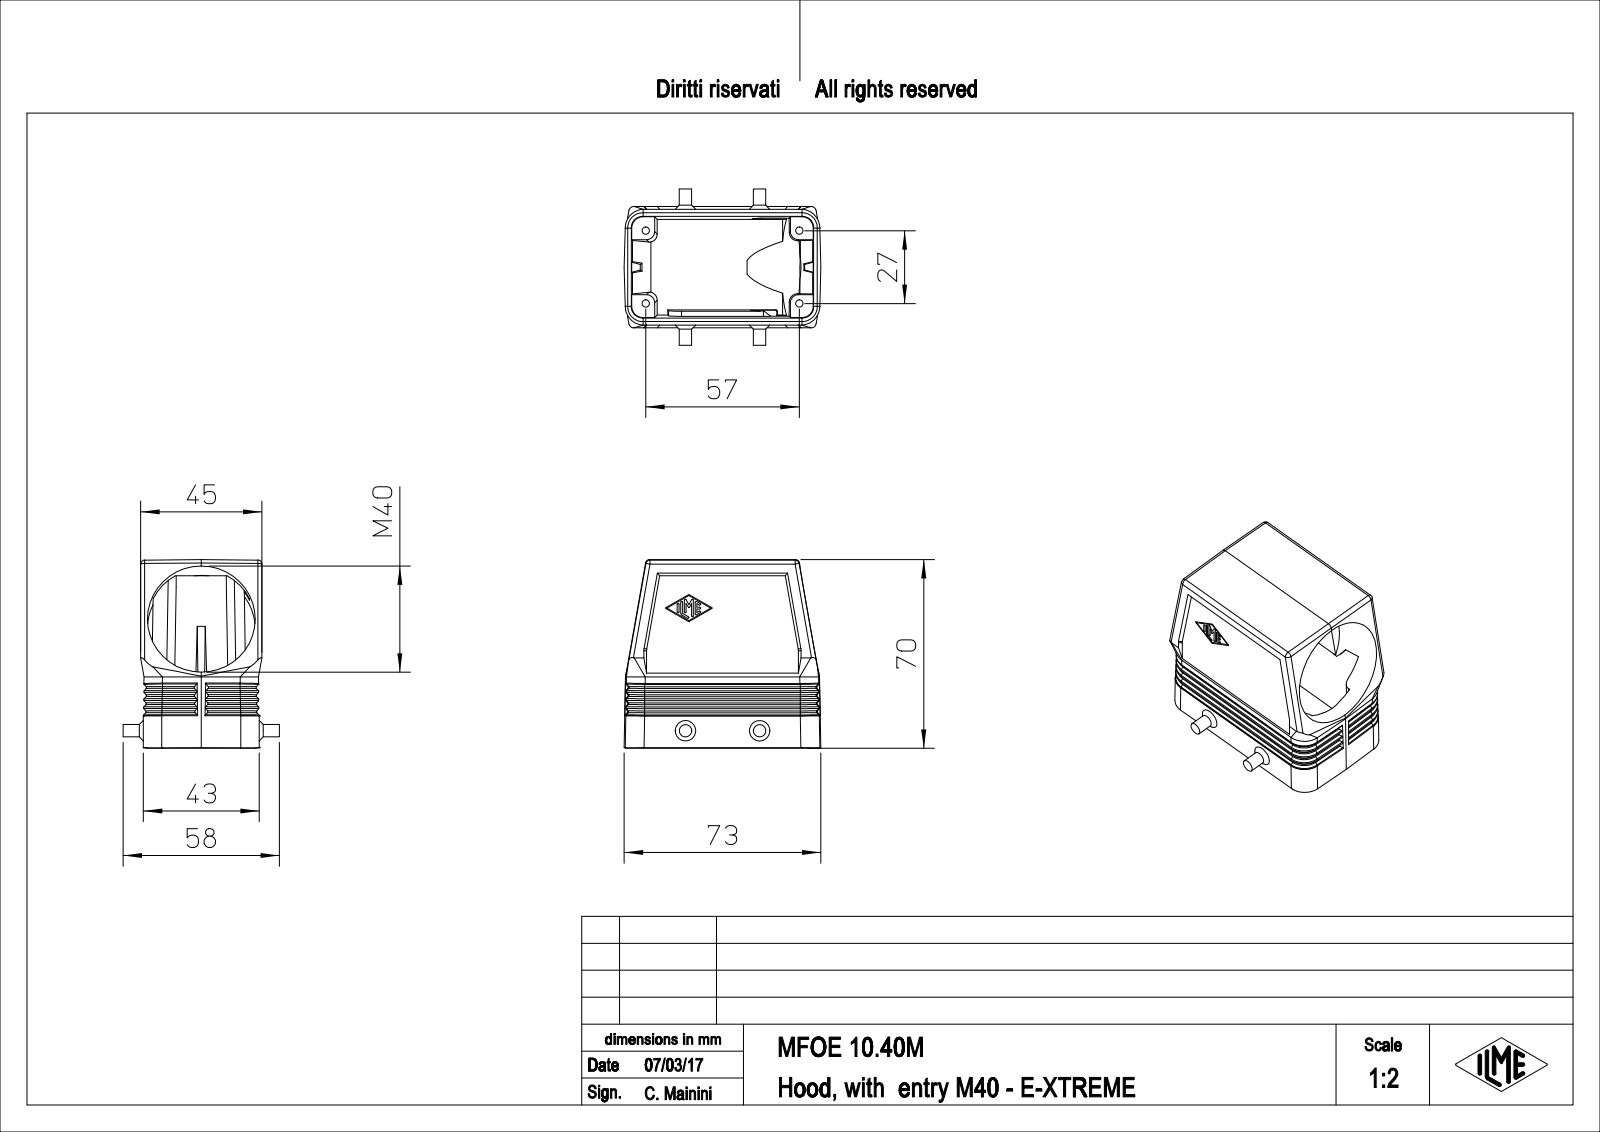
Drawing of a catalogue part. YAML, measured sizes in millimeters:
part_name: "MFOE_10.40M"
step_written_by: "PTC Creo Elements/Direct Modeling 19.0E 27-Jun-2016 (C) Parametric Technology GmbH (AUTOMOTIVE_DESIGN)"
units: millimeters
bodies: {solids: 1, faces: 359, planar: 145, cylindrical: 71, other: 143}
overall_size: [72.99, 70, 58]
volume: 60670
surface_area: 32411
round_holes:
  - {diameter: 2.75, count: 4}
  - {diameter: 40, count: 1}
round_bosses_or_shafts:
  - {diameter: 4.59, count: 2}
partial_cylinders:
  - {radius: 0.5, count: 17}
  - {radius: 1.5, count: 10}
  - {radius: 7, count: 8}
  - {radius: 3, count: 4}
  - {radius: 4.2, count: 4}
  - {radius: 6, count: 4}
  - {radius: 20, count: 1}
face_to_face_distances: [43, 8.5, 2, 1.91, 44, 1, 4, 45, 6, 11.35]
hole_center_spacings: [27, 57, 63.07]
